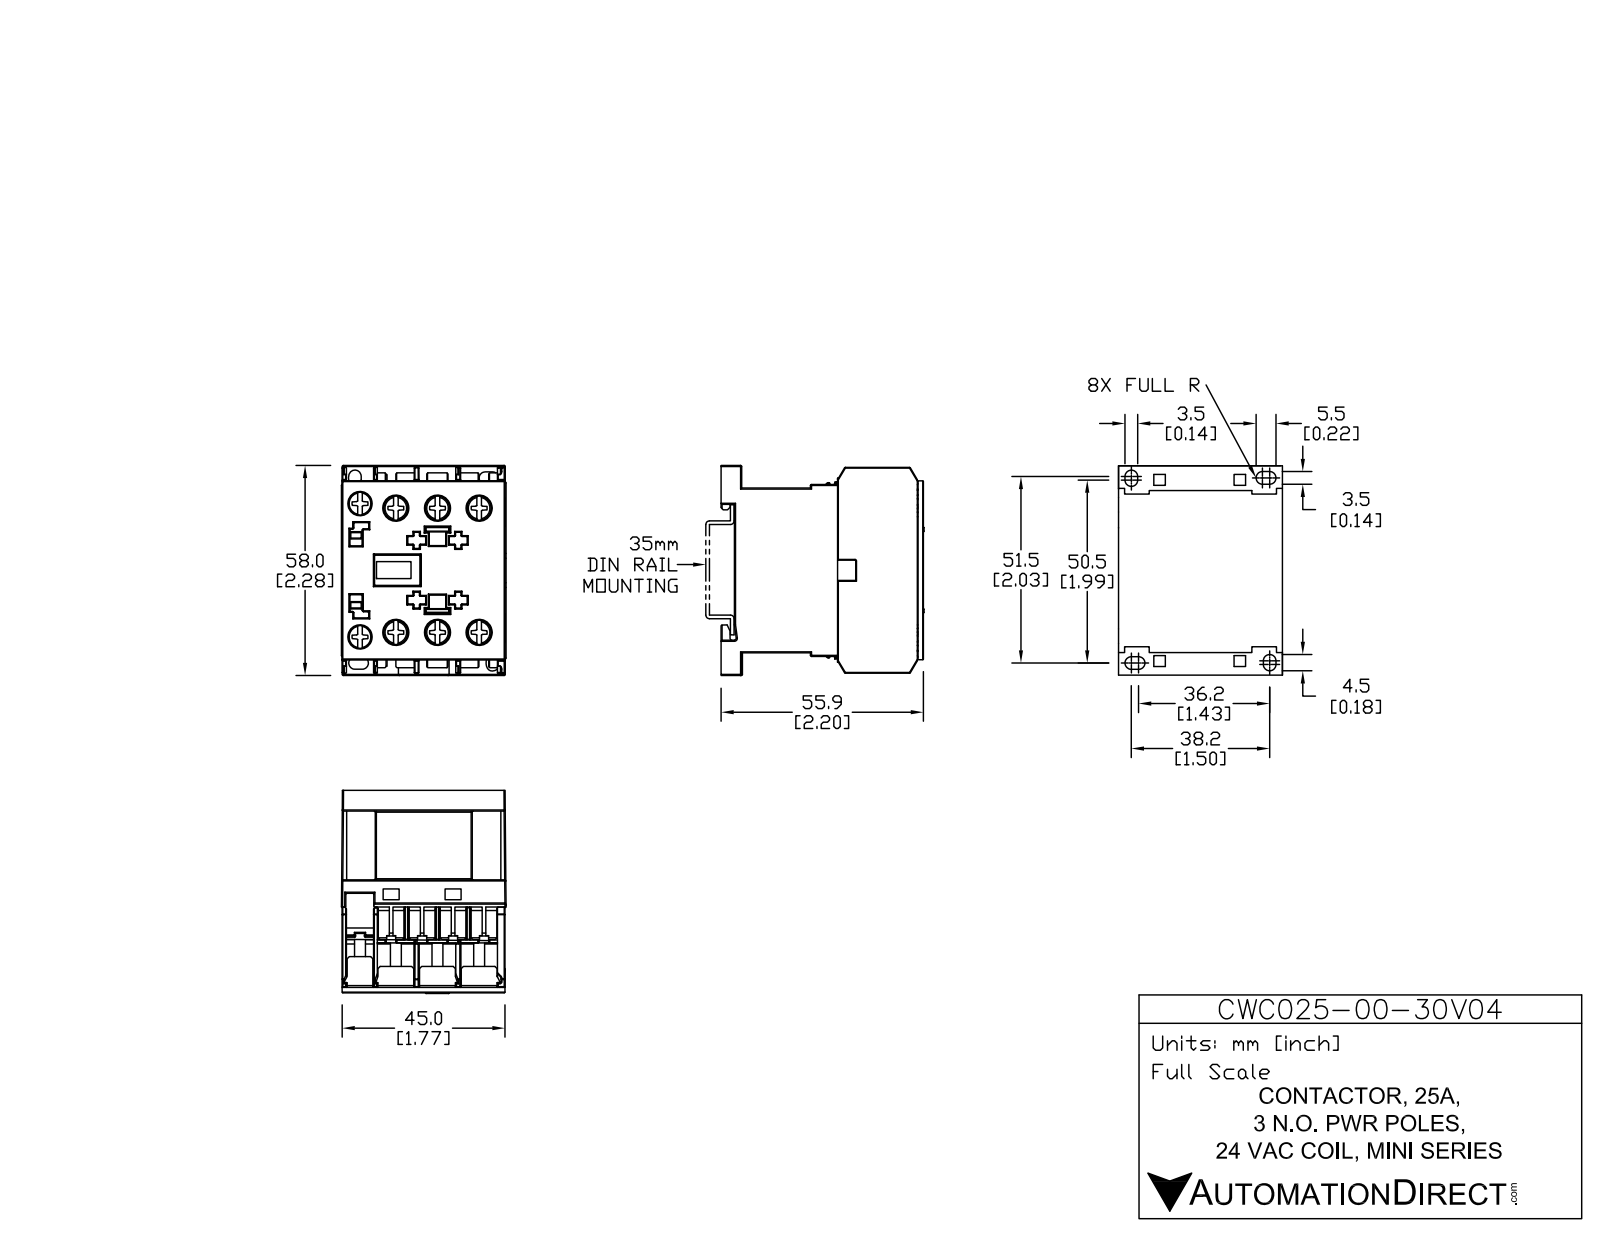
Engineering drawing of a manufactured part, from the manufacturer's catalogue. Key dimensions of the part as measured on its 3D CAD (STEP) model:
Part name (STEP PRODUCT): CWC025-00-30V04
STEP written by: SolidWorks 2013 (AUTOMOTIVE_DESIGN)
Units: millimetres
Bodies: 2 solids, 746 faces (639 planar, 107 cylindrical, 0 other)
Overall size (bounding box): 58 × 55.7 × 45
Volume: 92 387 mm³ · Surface area: 34 434 mm²
Round holes (diameter × count): ⌀6.85 ×6, ⌀6.5 ×2
Round bosses / shafts (diameter × count): ⌀6.5 ×6, ⌀3.5 ×6, ⌀5.25 ×2, ⌀2.75 ×2
Partial cylindrical surfaces — rounded edges, fillets, slot ends (radius × count): R0.2 ×14, R0.5 ×10, R1.72 ×8, R0.3 ×7
Main face-to-face distances: 45, 1, 23.5, 28.5, 28.53, 52, 23.47, 37.35, 8.85, 8.82
Hole centre spacings: 11.5, 36.37, 34.5, 9.55, 21.02, 23, 32.52, 36.75
